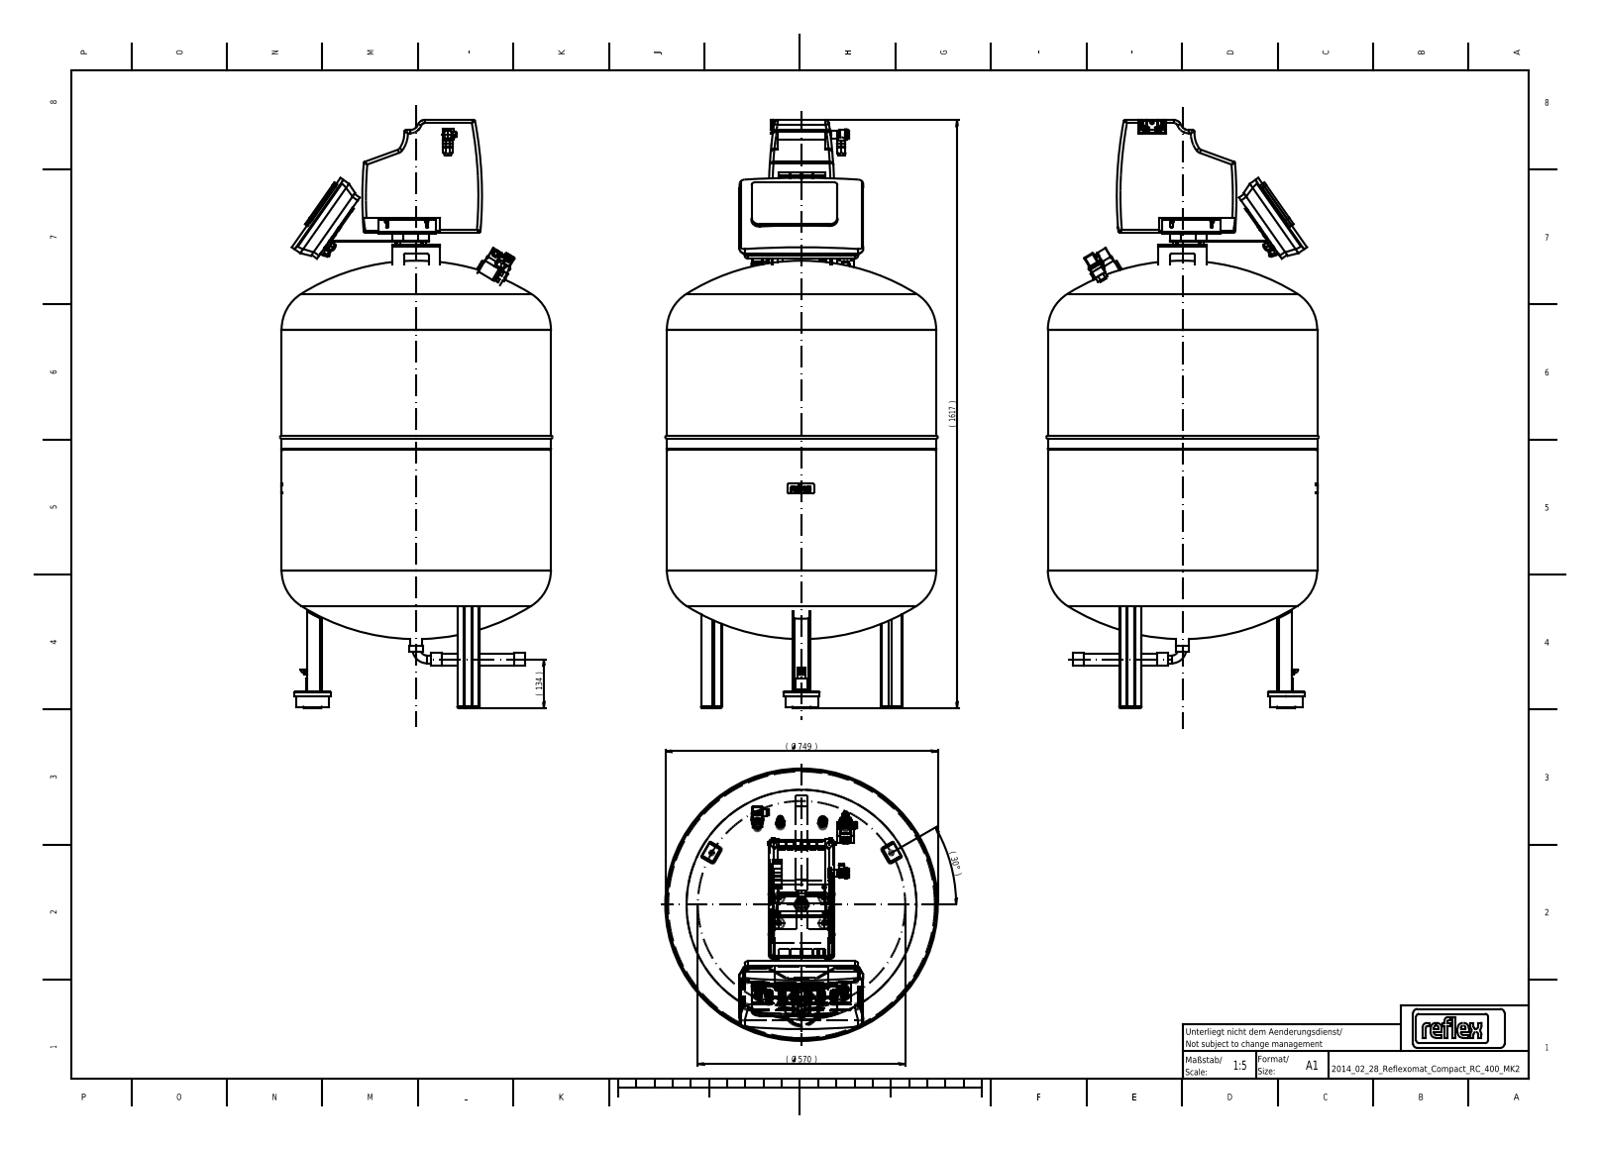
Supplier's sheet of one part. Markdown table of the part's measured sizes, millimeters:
| quantity | value |
| --- | --- |
| STEP written by | Mechanical Desktop 2011 (CONFIG_CONTROL_DESIGN) |
| units | millimeters |
| bodies | 42 solids, 2542 faces (1705 planar, 419 cylindrical, 418 other) |
| overall size | 1617 × 748.8 × 748.8 |
| volume | 412 800 000 mm³ |
| surface area | 6 074 000 mm² |
| round holes (diameter × count) | 8.2 × 8, 10.5 × 8, 17 × 7, 5.5 × 4, 9 × 4, 10 × 2, 13.4 × 2, 2 × 1, 6.5 × 1, 7 × 1, 14 × 1, 20 × 1 |
| round bosses / shafts (diameter × count) | 19 × 8, 16 × 8, 8 × 8, 17.5 × 7, 30 × 4, 21.3 × 3, 19.8 × 3, 35 × 2 |
| partial cylindrical surfaces (radius × count) | 2.5 × 31, 5 × 23, 8 × 14, 10 × 11, 1 × 10, 3 × 6, 3.94 × 4, 4.5 × 4 |
| main face-to-face distances | 662, 4, 2.5, 22, 2, 47.5, 928, 266, 26, 906 |
| hole center spacings | 125, 36, 22, 70, 72, 125.14, 126.92, 128.1 |
